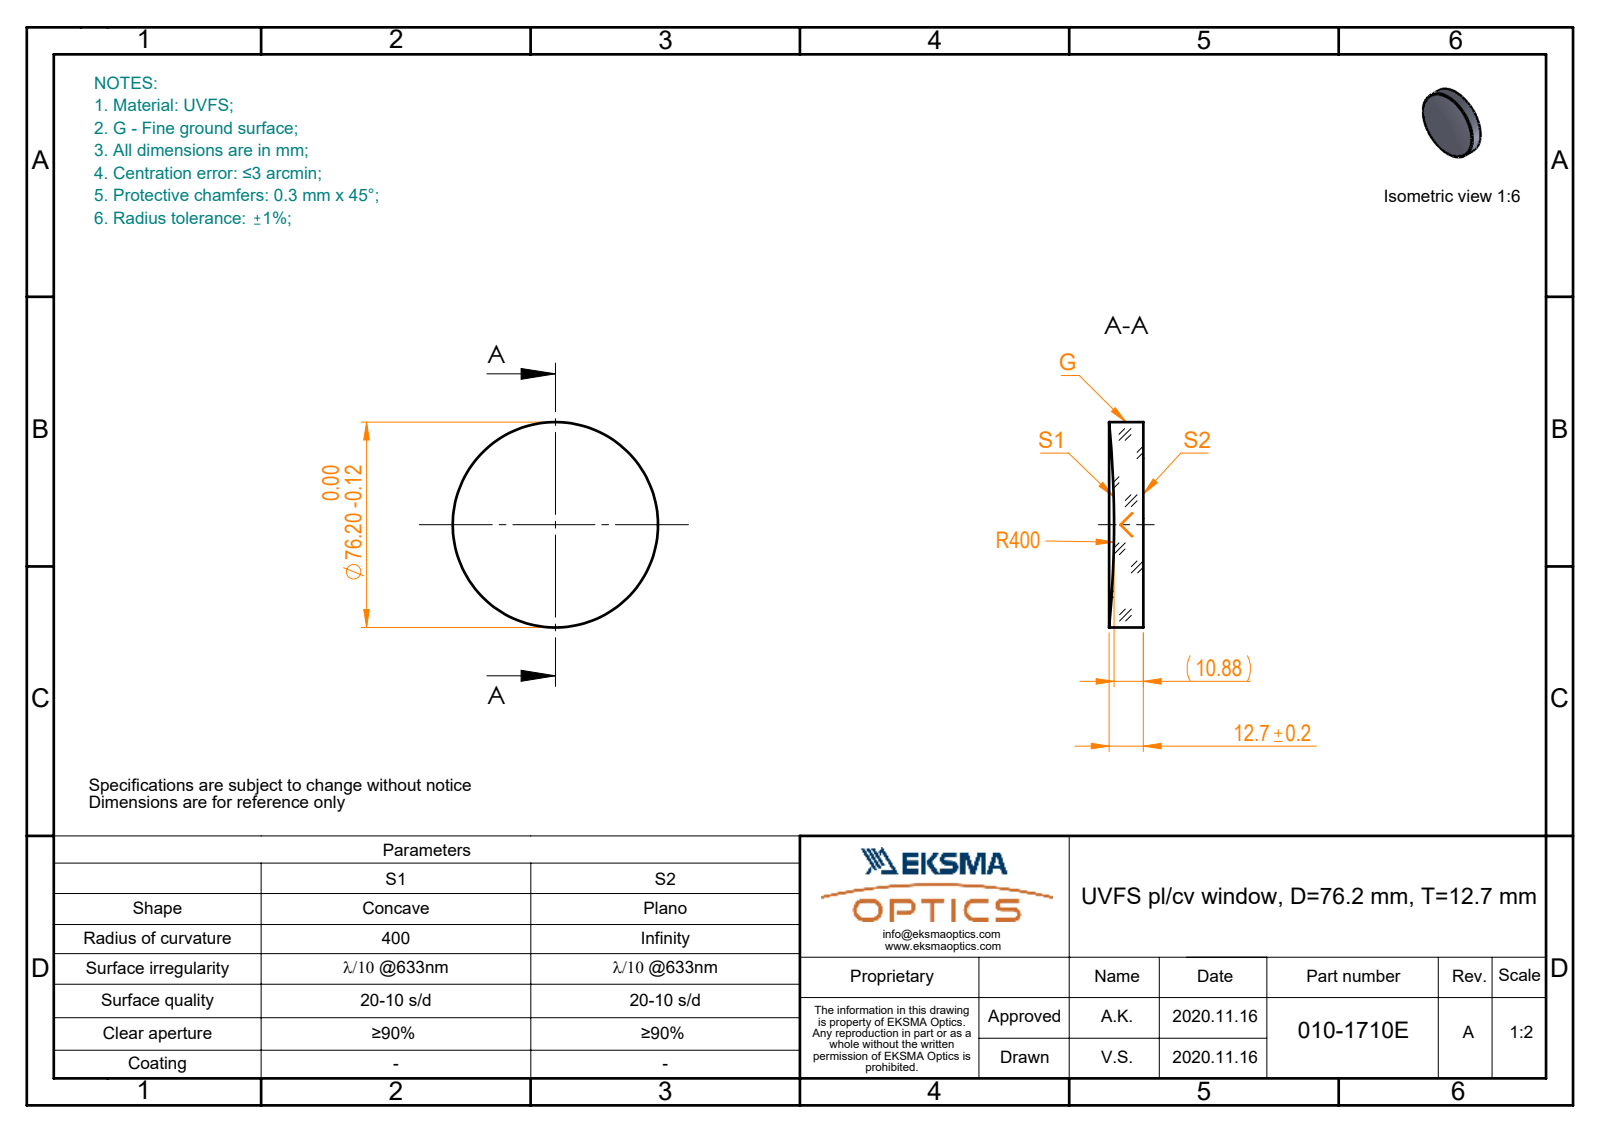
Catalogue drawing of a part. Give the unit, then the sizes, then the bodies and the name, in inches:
Units: inches
Overall size (bounding box): 3 × 3 × 0.5
Round bosses / shafts (diameter × count): ⌀3 ×1
Volume: 3.281 in³ · Surface area: 18.87 in²
Bodies: 1 solid, 5 faces (1 planar, 2 cylindrical, 2 other)
Part name (STEP PRODUCT): 010-1710E_UVFS_PCV_window
STEP written by: SolidWorks 2019 (CONFIG_CONTROL_DESIGN)
